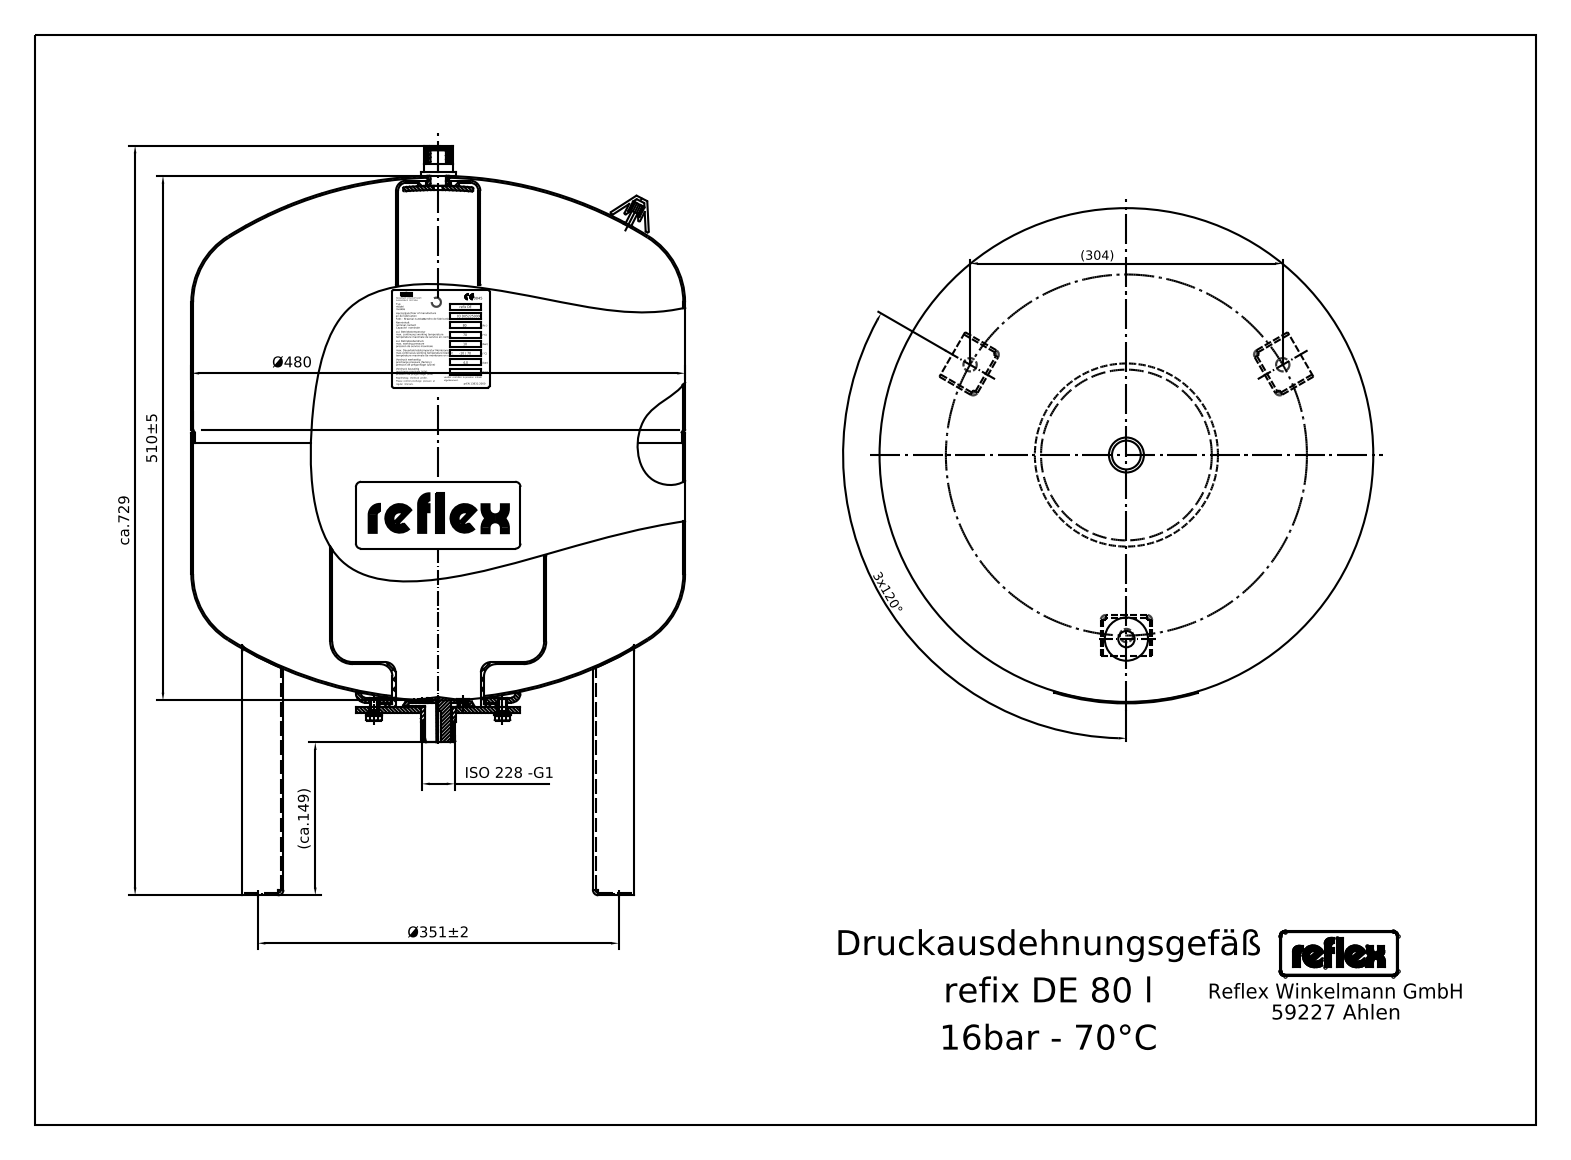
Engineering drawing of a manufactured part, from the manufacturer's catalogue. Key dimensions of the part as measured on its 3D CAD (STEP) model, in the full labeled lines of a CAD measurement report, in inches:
STEP written by: Mechanical Desktop 2008 (CONFIG_CONTROL_DESIGN)
Units: inches
Bodies: 17 solids, 367 faces (166 planar, 131 cylindrical, 70 other)
Overall size (bounding box): 28.701 × 18.898 × 18.898
Volume: 4 636 in³ · Surface area: 3 002 in²
Round holes (diameter × count): ⌀0.528 ×3, ⌀0.555 ×1, ⌀3.504 ×1, ⌀5.906 ×1
Round bosses / shafts (diameter × count): ⌀0.315 ×6, ⌀18.898 ×1, ⌀6.299 ×1, ⌀5.512 ×1, ⌀1.339 ×1, ⌀1.327 ×1, ⌀0.673 ×1, ⌀0.63 ×1
Partial cylindrical surfaces — rounded edges, fillets, slot ends (radius × count): R0.039 ×15, R0.098 ×15, R0.197 ×15, R0.155 ×4, R0.062 ×3, R0.106 ×2, R0.186 ×2, R0.256 ×2
Main face-to-face distances: 9.449, 0.098, 1.87, 0.197, 1.772, 1.969, 5.591, 15.039, 5.787, 15.236
Hole centre spacings: 6.909, 11.968
